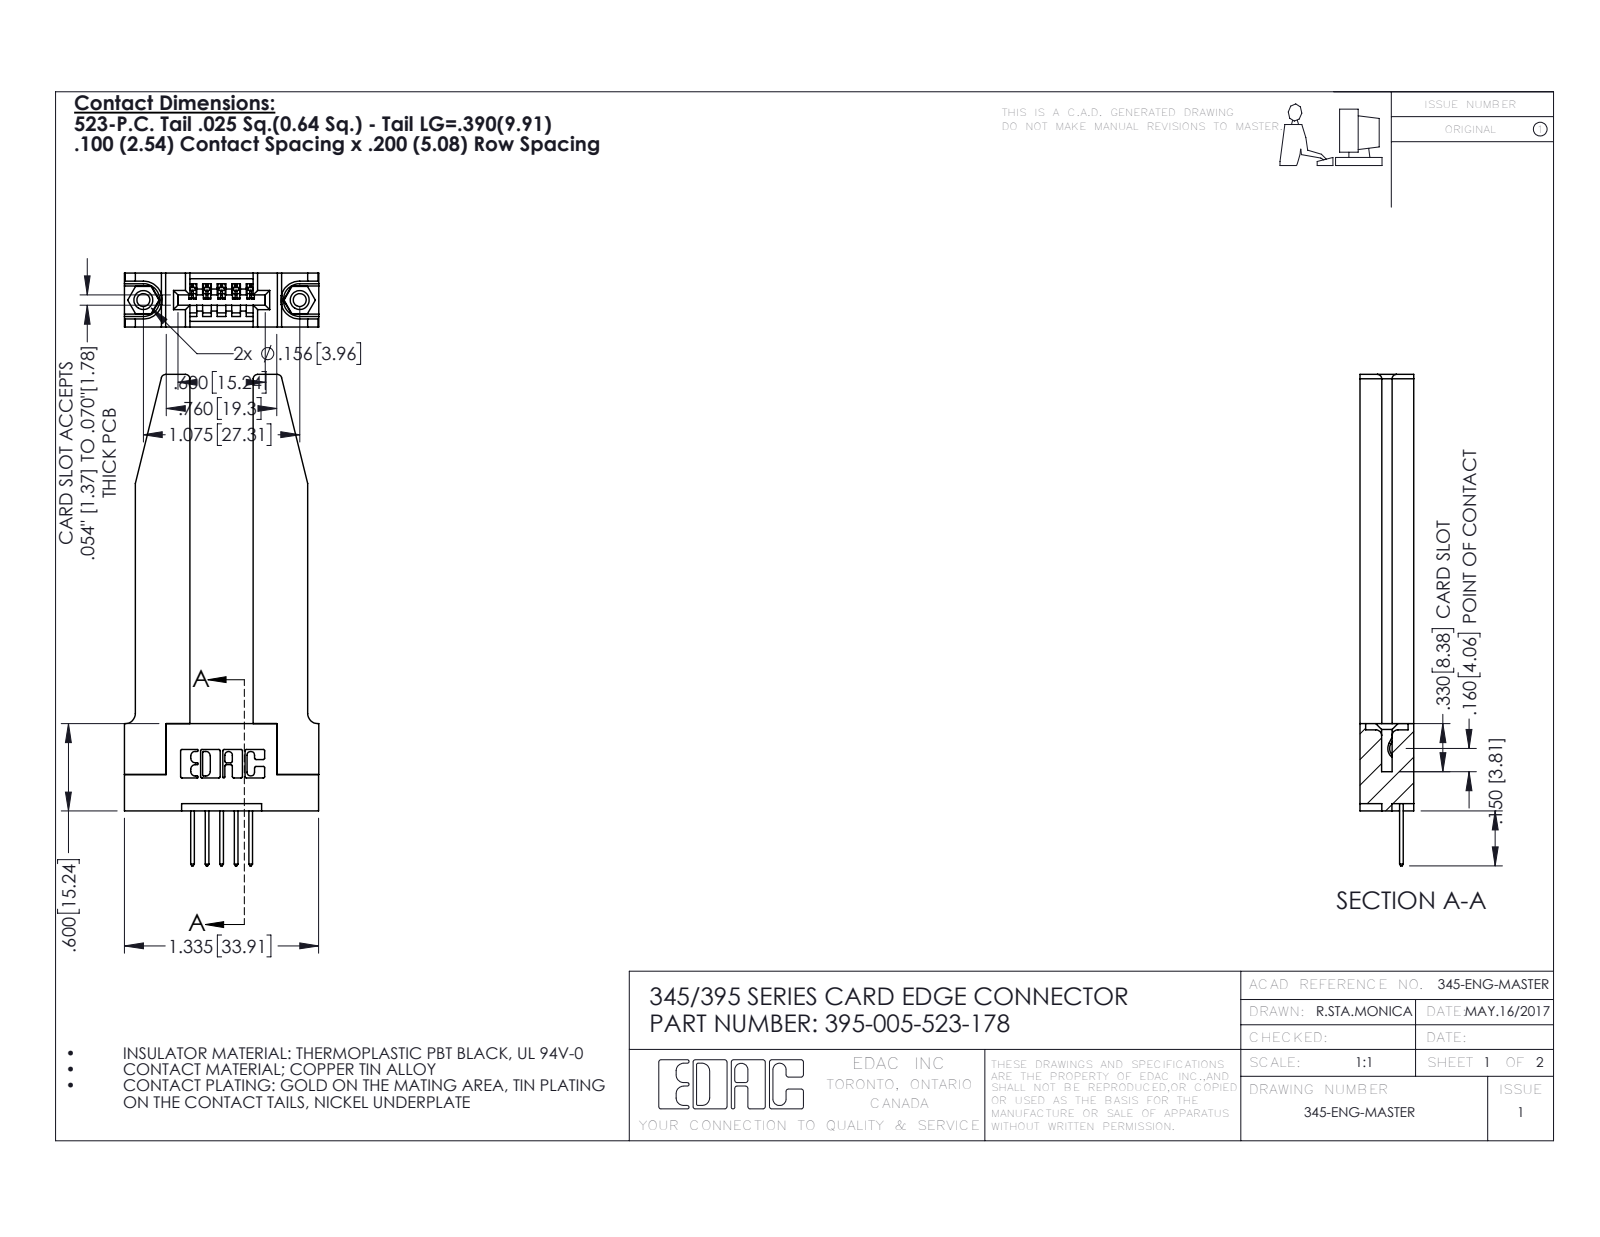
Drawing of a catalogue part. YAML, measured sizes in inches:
part_name: "395-005-523-178; 345 Part_Flush Mounting Lugs - 0.156 Dia-TH; 345-220-078_345-220-078; 345-292-001_345-293-123 (+1 more)"
step_written_by: "SolidWorks 2016 (CONFIG_CONTROL_DESIGN)"
units: inches
bodies: {solids: 10, faces: 650, planar: 422, cylindrical: 176, other: 52}
overall_size: [3.377, 1.336, 0.37]
volume: 0.652
surface_area: 15.85
round_holes:
  - {diameter: 0.089, count: 2}
  - {diameter: 0.125, count: 2}
  - {diameter: 0.156, count: 2}
  - {diameter: 0.064, count: 1}
round_bosses_or_shafts:
  - {diameter: 0.155, count: 2}
partial_cylinders:
  - {radius: 0.01, count: 22}
  - {radius: 0.006, count: 10}
  - {radius: 0.01, count: 10}
  - {radius: 0.03, count: 8}
  - {radius: 0.007, count: 6}
  - {radius: 0.031, count: 6}
  - {radius: 0.026, count: 3}
  - {radius: 0.031, count: 2}
face_to_face_distances: [0.37, 0.15, 0.22, 0.435, 0.148, 0.072, 0.2, 0.077, 0.298, 0.095]
hole_center_spacings: [0.27, 0.847, 1.075]
